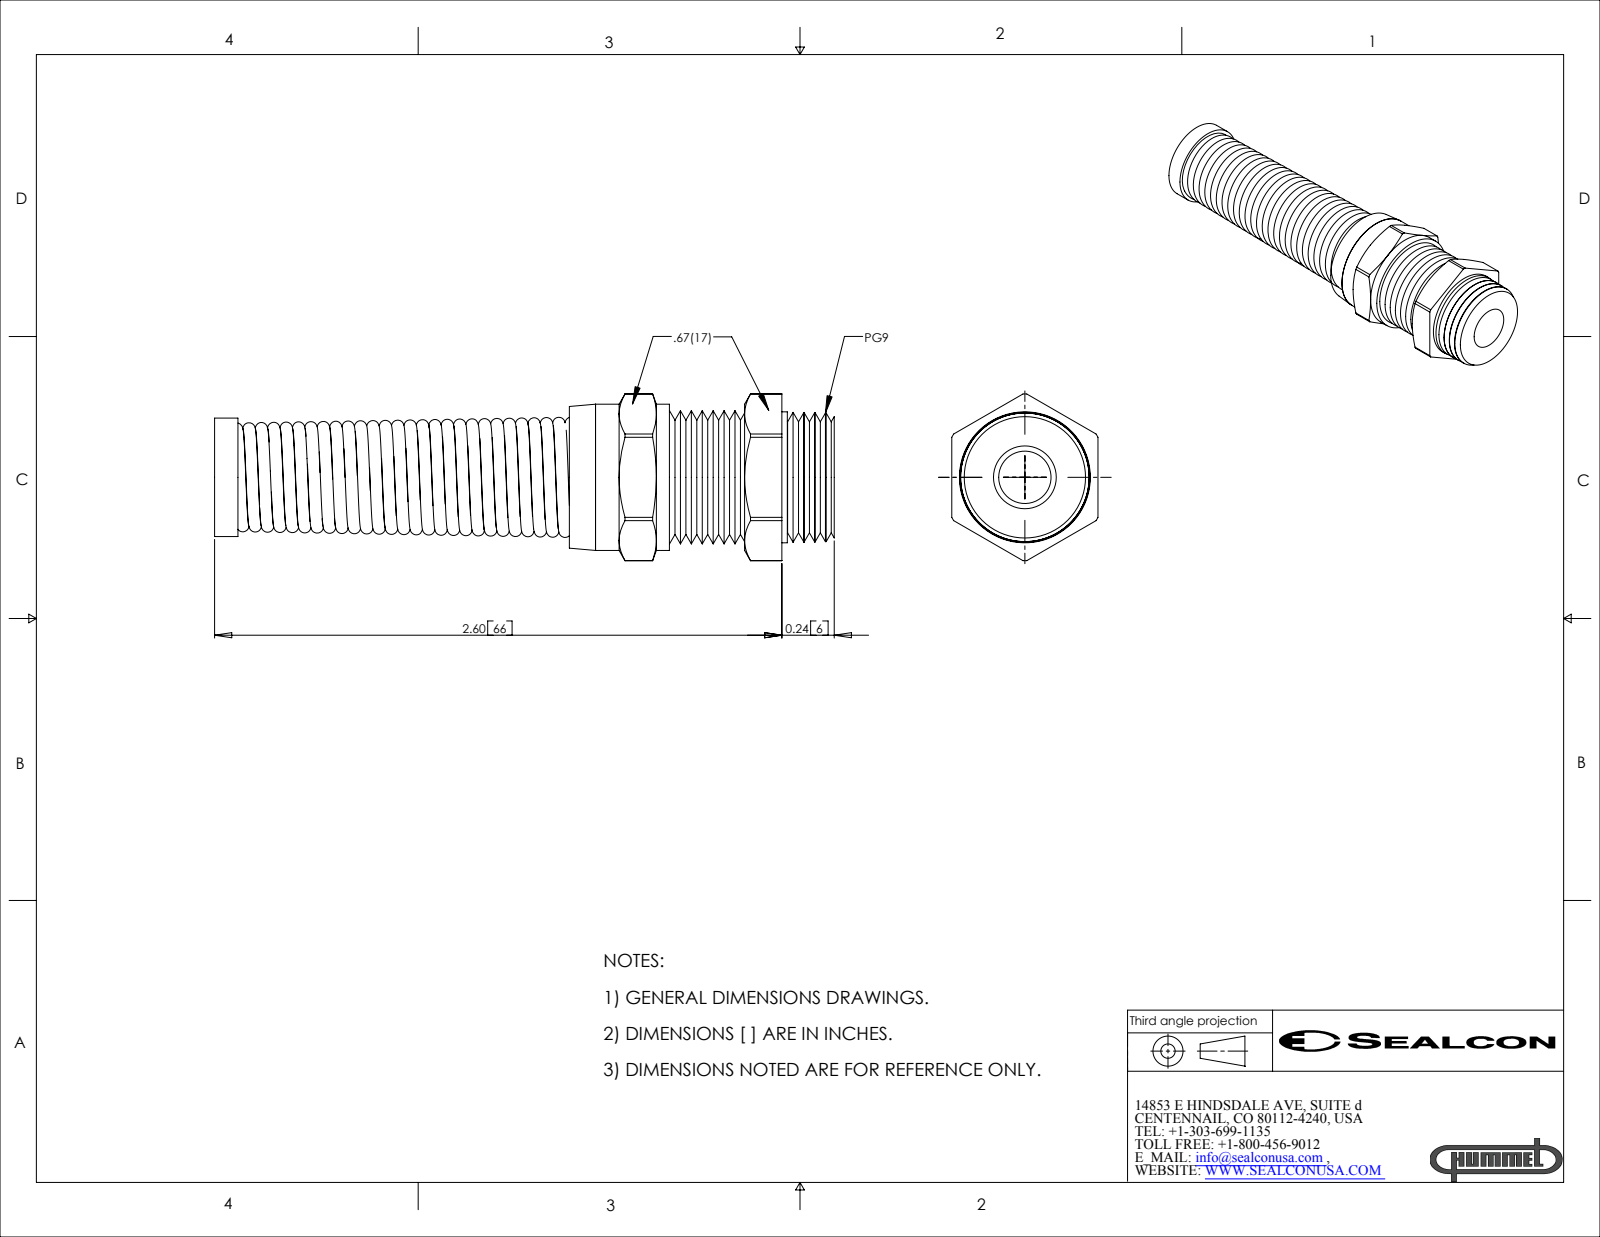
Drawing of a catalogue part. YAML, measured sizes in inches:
part_name: "CF09AR-BR"
step_written_by: "SolidWorks 2007 (CONFIG_CONTROL_DESIGN)"
units: inches
bodies: {solids: 3, faces: 201, planar: 26, cylindrical: 32, other: 143}
overall_size: [2.84, 0.764, 0.67]
volume: 0.577
surface_area: 12.03
round_holes:
  - {diameter: 0.24, count: 1}
  - {diameter: 0.612, count: 1}
round_bosses_or_shafts:
  - {diameter: 0.67, count: 1}
  - {diameter: 0.6, count: 1}
  - {diameter: 0.543, count: 1}
partial_cylinders:
  - {radius: 0.382, count: 1}
face_to_face_distances: [0.67, 0.108, 1.746, 1.854, 2.84, 1.094, 0.986, 1.786, 0.04, 0.068]
